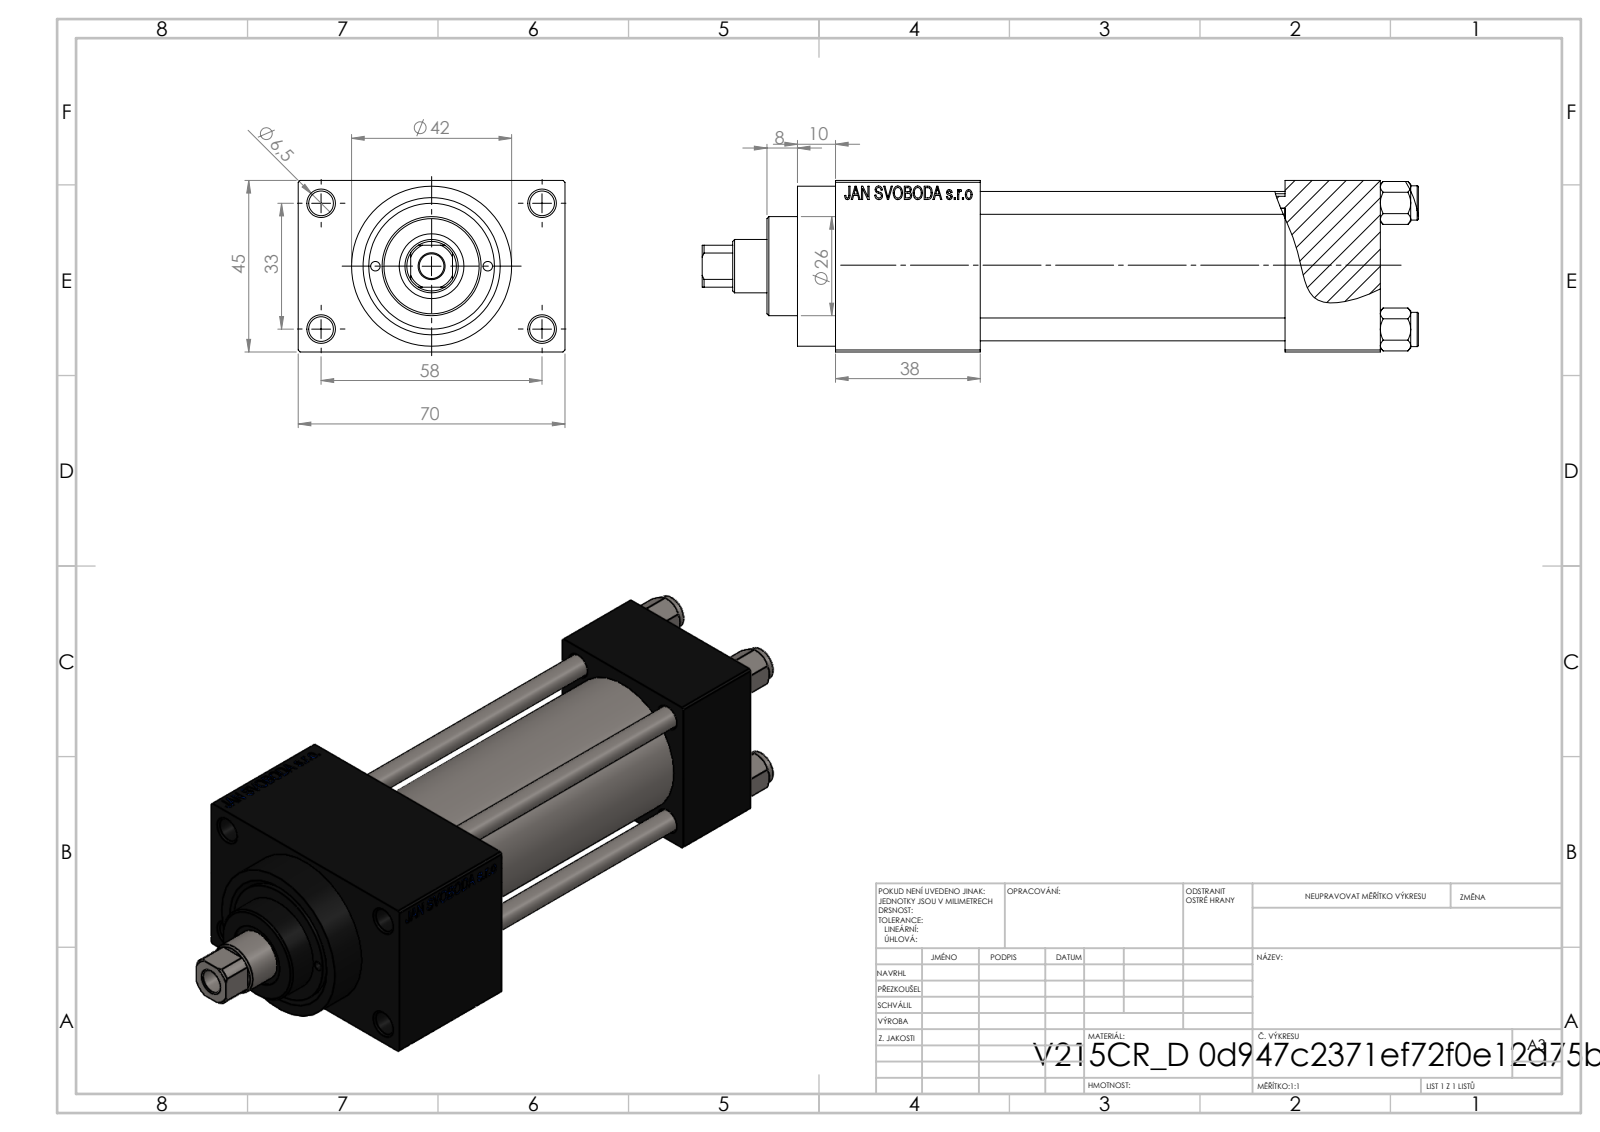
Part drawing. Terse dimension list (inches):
name: V215CR_D_Body; V215CR_VCP_D; NUT_M5_D; V215_VC_A (+1 more)
written by: SolidWorks 2019 (CONFIG_CONTROL_DESIGN)
unit: in
bodies: 10 solids, 1110 faces (498 planar, 92 cylindrical, 520 other)
size: 7.402 × 2.756 × 1.772
volume: 5.598 in³; area: 132.6 in²
holes: 5× ⌀0.256, 4× ⌀0.236, 2× ⌀0.098, 2× ⌀0.276, 2× ⌀0.518, 2× ⌀0.787, 1× ⌀0.551, 1× ⌀0.669, 1× ⌀0.945, 1× ⌀1.26, 1× ⌀1.299
bosses: 4× ⌀0.354, 1× ⌀1.654, 1× ⌀1.496, 1× ⌀1.024
rounds: 1× R0.256
face distances: 1.772, 0.984, 0.492, 3.15, 4.134, 2.264, 4.646, 1.496, 5.63, 2.756
hole spacings: 0.488, 0.657, 0.858, 0.924, 1.307, 1.314, 1.392, 1.396
